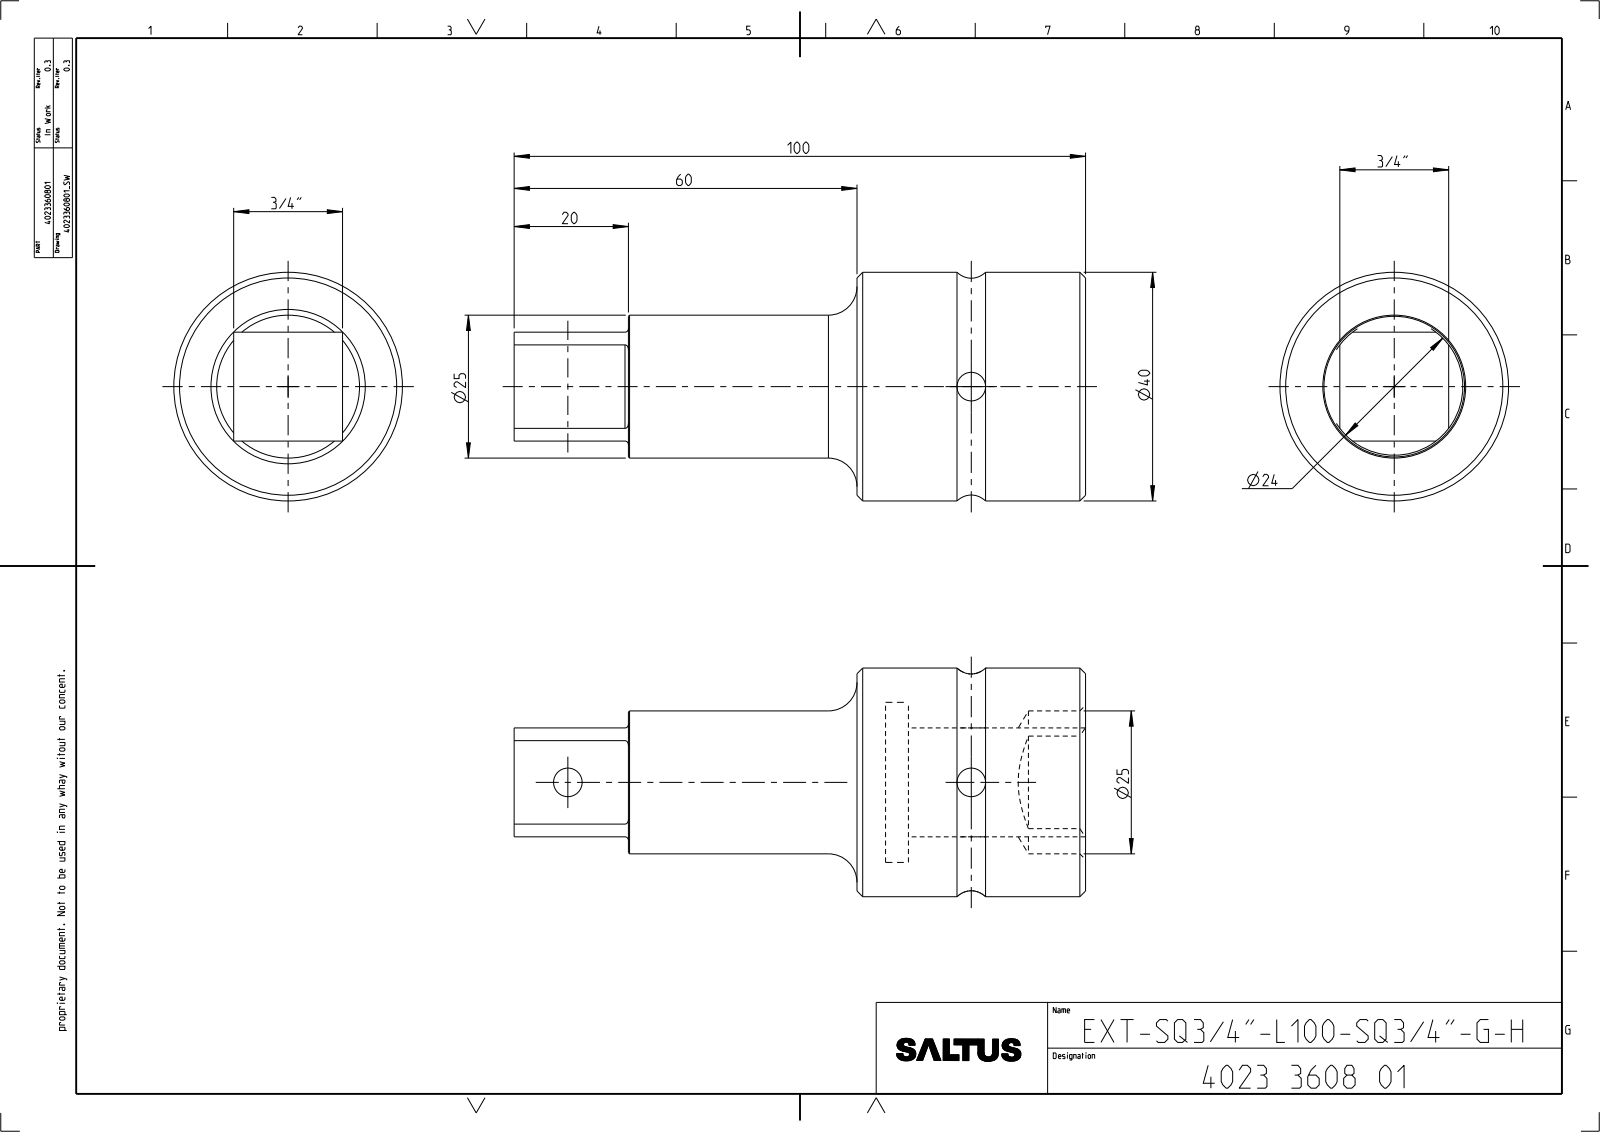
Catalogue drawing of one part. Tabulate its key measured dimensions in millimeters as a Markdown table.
| quantity | value |
| --- | --- |
| part name | 4023360801 |
| STEP written by | CREO PARAMETRIC BY PTC INC, 2022414 (CONFIG_CONTROL_DESIGN) |
| units | millimeters |
| bodies | 1 solid, 50 faces (12 planar, 24 cylindrical, 14 other) |
| overall size | 100 × 40 × 40 |
| volume | 57 616 mm³ |
| surface area | 14 677 mm² |
| round holes (diameter × count) | 6 × 2, 25 × 1 |
| round bosses / shafts (diameter × count) | 40 × 1 |
| partial cylindrical surfaces (radius × count) | 12.45 × 1, 12.8 × 1 |
| main face-to-face distances | 19.09, 19.18, 19, 34, 100, 66, 77, 43, 23 |
| hole center spacings | 67 |
